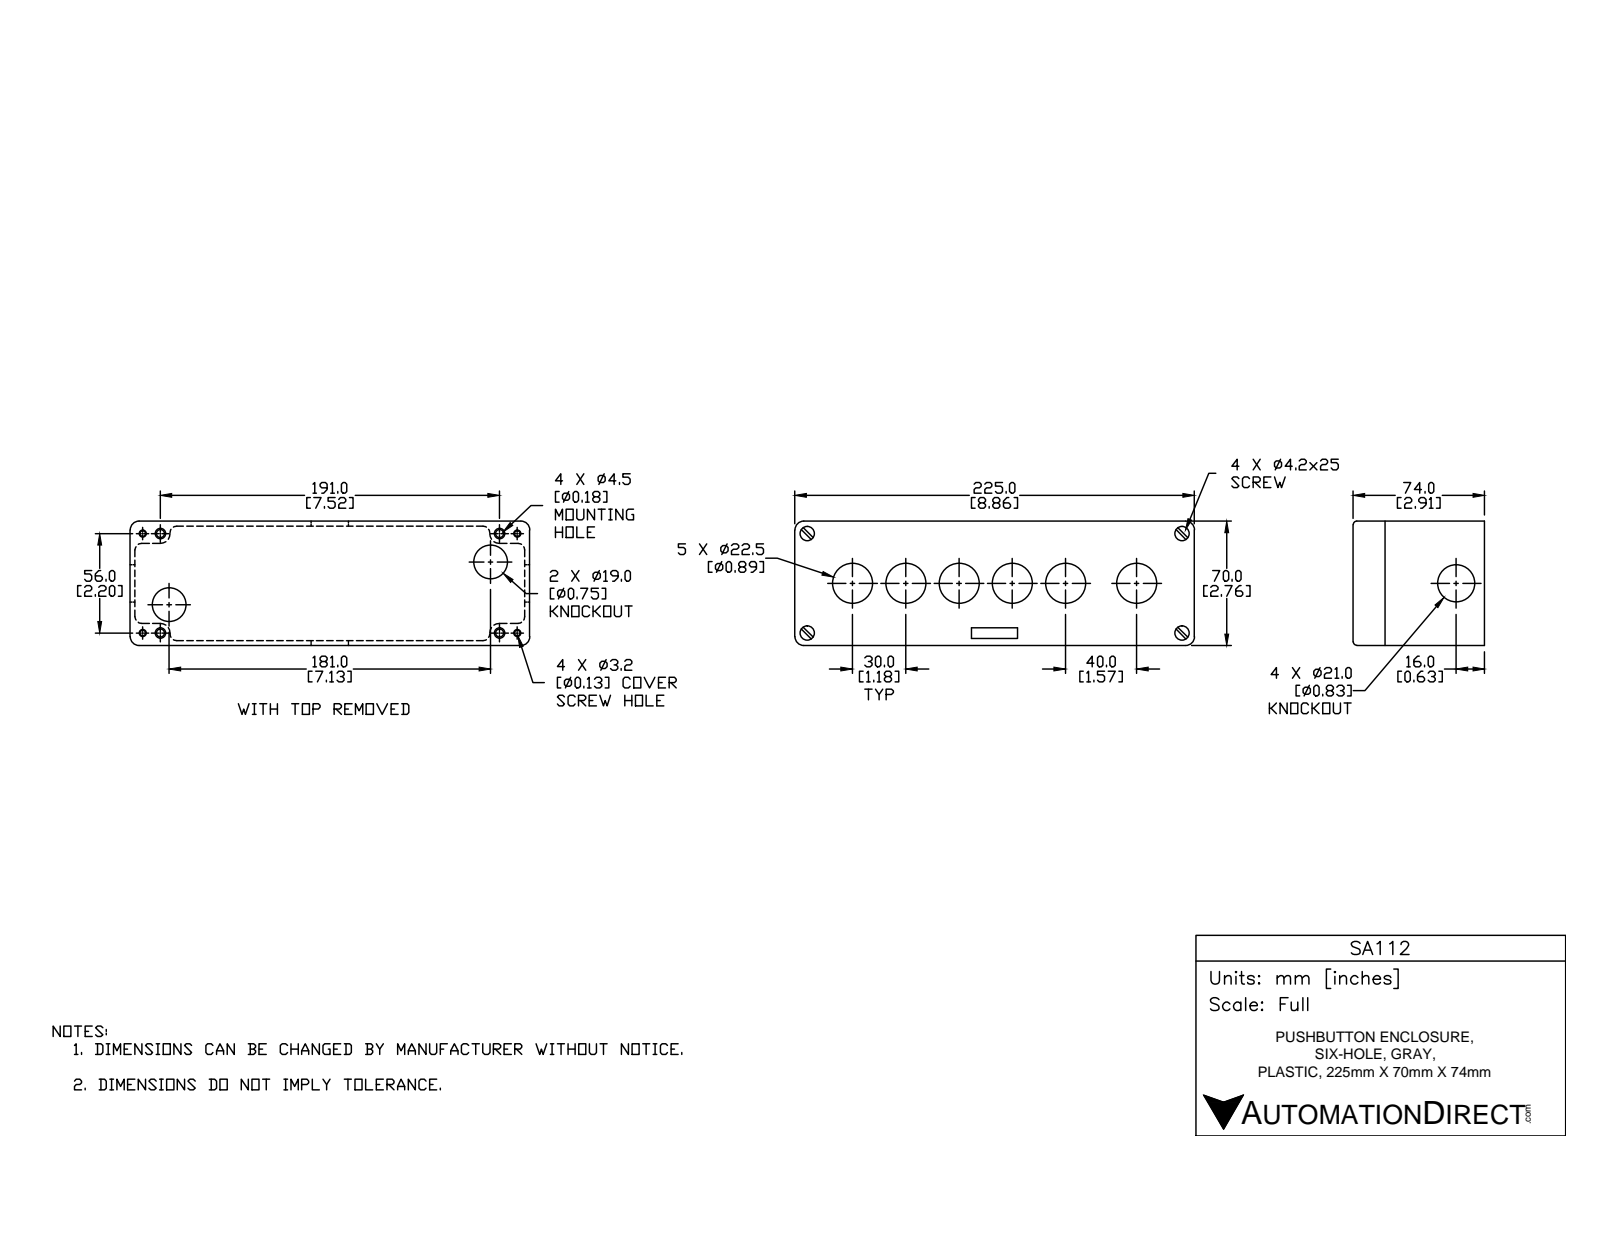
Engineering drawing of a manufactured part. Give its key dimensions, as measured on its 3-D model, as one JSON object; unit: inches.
{"part_name": "SA112", "step_written_by": "SolidWorks 2018 (AUTOMOTIVE_DESIGN)", "units": "inches", "bodies": {"solids": 6, "faces": 502, "planar": 134, "cylindrical": 204, "other": 164}, "overall_size": [8.858, 2.915, 2.756], "volume_in3": 16.43, "surface_area_in2": 229.3, "round_holes": [[0.886, 6], [0.126, 4], [0.169, 4], [0.177, 4], [0.295, 4], [0.315, 4], [0.094, 2], [0.748, 2], [0.827, 2]], "round_bosses_or_shafts": [[0.291, 4], [0.11, 4]], "partial_cylinders_radius": [[0.02, 16], [0.033, 8], [0.117, 8], [0.039, 4], [0.071, 4], [0.197, 4], [0.247, 4], [0.331, 4]], "face_to_face_distances": [2.756, 0.139, 0.098, 2.915, 2.817, 2.617, 0.139, 2.478, 2.617, 2.738], "hole_center_spacings": [1.12, 7.913, 0.394, 1.181, 1.26, 1.491, 2.205, 2.24]}
